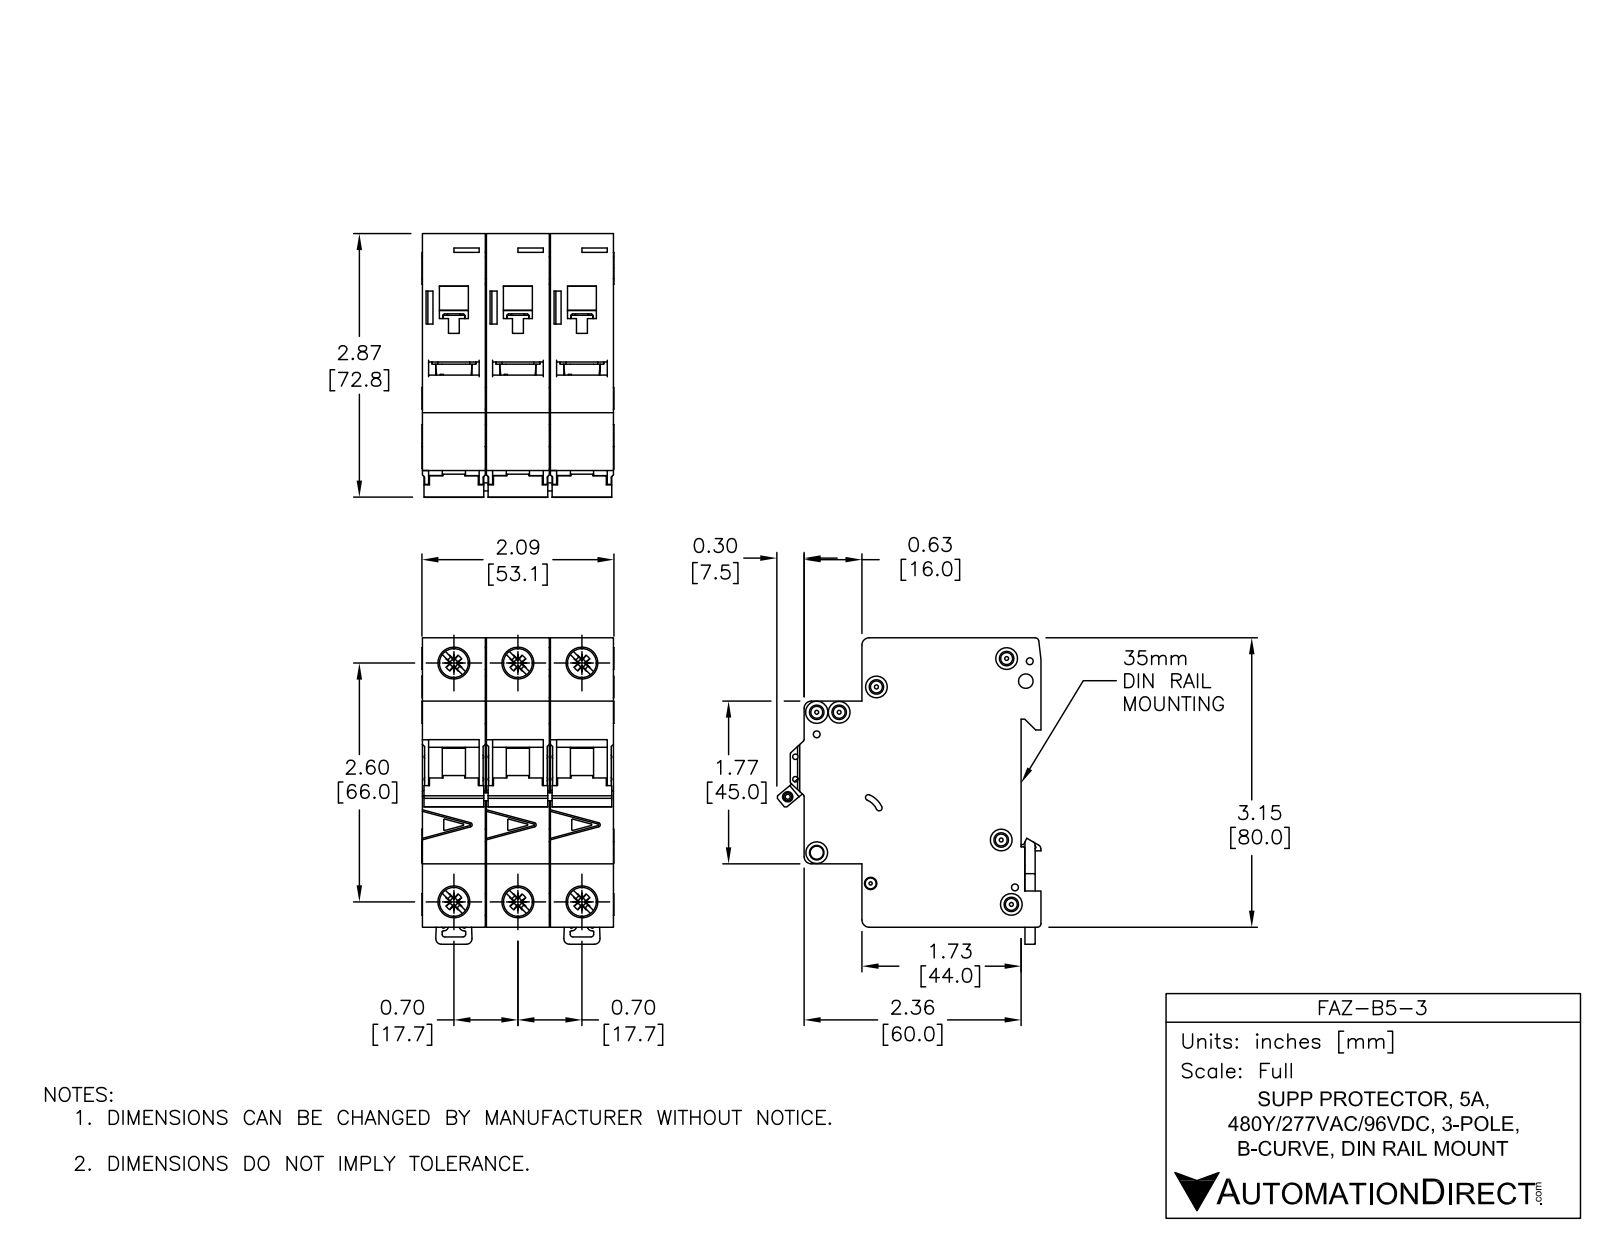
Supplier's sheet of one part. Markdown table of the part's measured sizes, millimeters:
| quantity | value |
| --- | --- |
| part name | FAZ-B5-3 |
| STEP written by | SolidWorks 2014 (AUTOMOTIVE_DESIGN) |
| units | millimeters |
| bodies | 11 solids, 1650 faces (697 planar, 590 cylindrical, 363 other) |
| overall size | 84.78 × 73.04 × 53.1 |
| volume | 224 680 mm³ |
| surface area | 58 052 mm² |
| round holes (diameter × count) | 3.6 × 6, 8.2 × 4, 1.9 × 3, 1.09 × 2, 1.5 × 2, 4 × 2, 7.15 × 2, 2.15 × 1, 2.2 × 1, 2.55 × 1, 3.3 × 1, 3.4 × 1 |
| round bosses / shafts (diameter × count) | 6 × 4, 2.5 × 3, 8.2 × 2 |
| partial cylindrical surfaces (radius × count) | 0.25 × 68, 0.5 × 25, 1 × 12, 2 × 12, 0.2 × 11, 1.8 × 3, 0.8 × 2, 3 × 2 |
| main face-to-face distances | 17.7, 17.5, 35.4, 35.2, 52.9, 17.9, 79.48, 5.5, 49.5, 44 |
| hole center spacings | 17.7, 68.33, 66, 6.2, 13.64, 35.4, 74.89, 4.81 |
